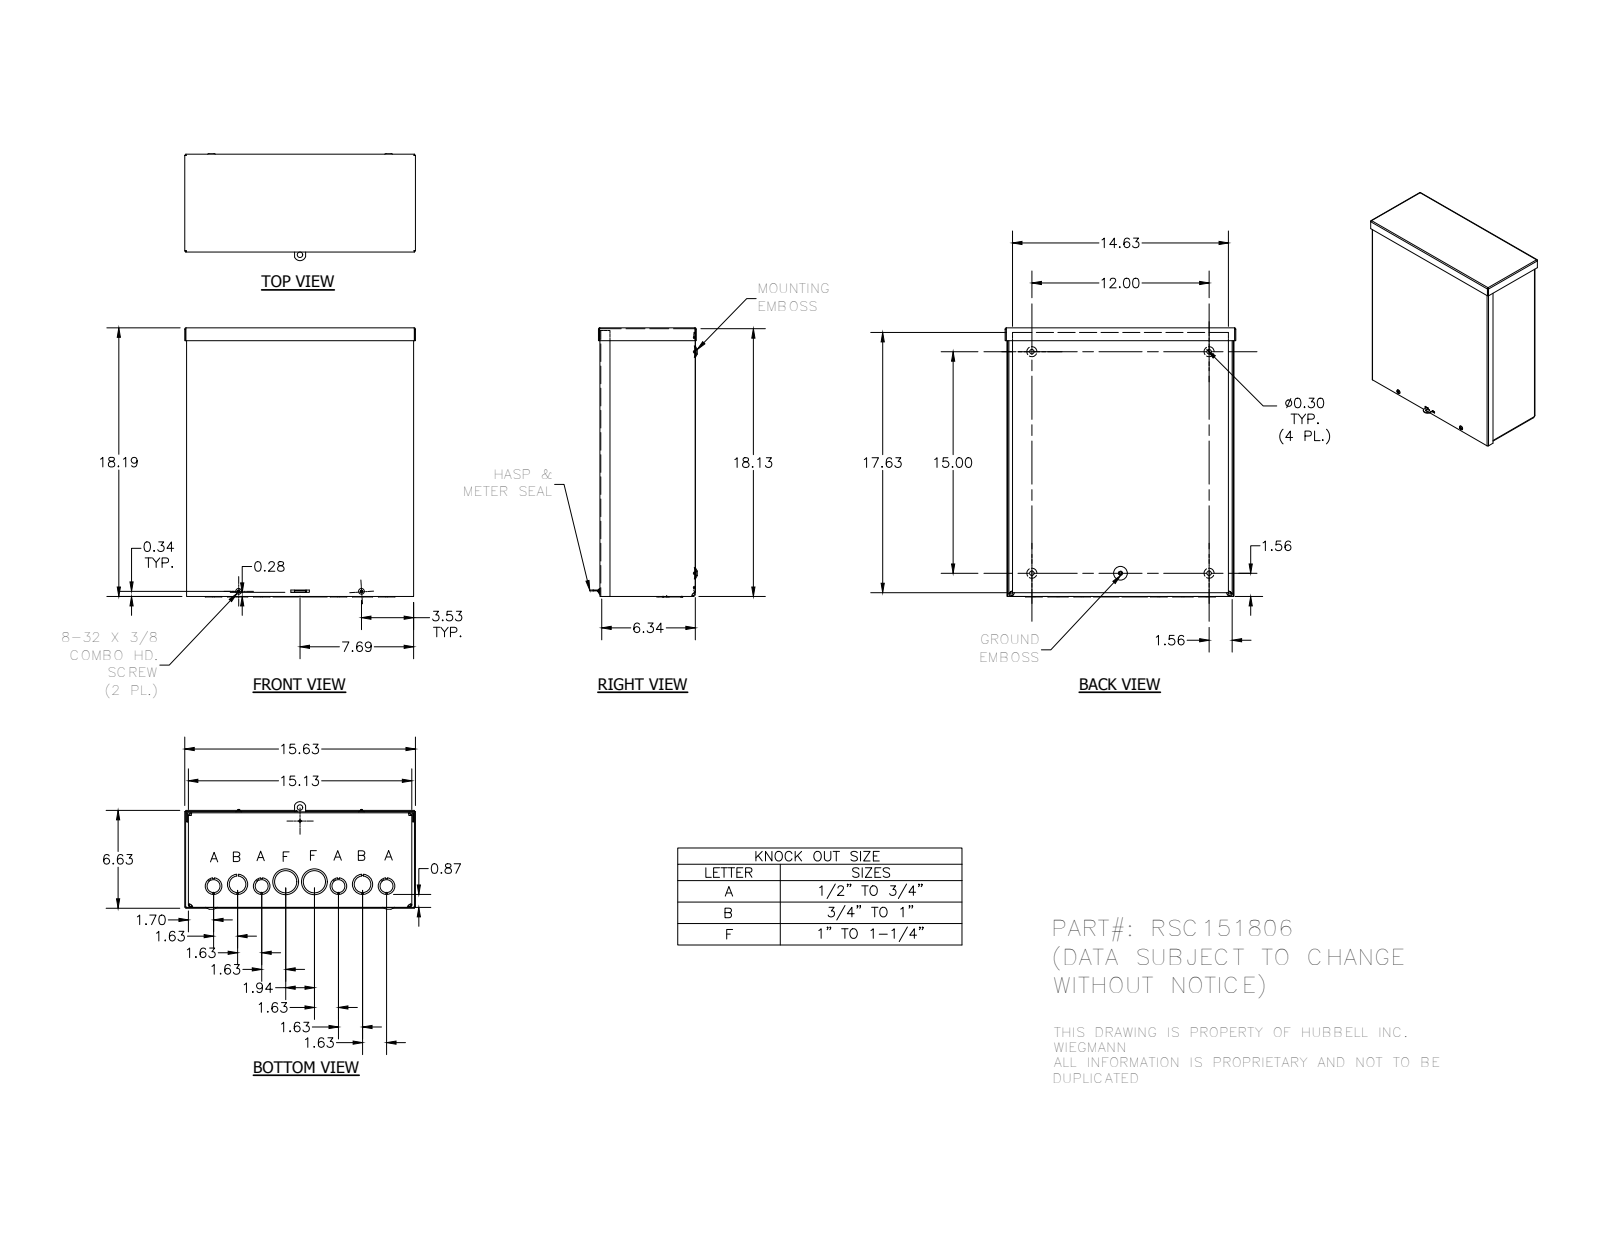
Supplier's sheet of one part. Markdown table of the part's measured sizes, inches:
| quantity | value |
| --- | --- |
| part name | RSC151806; RSC151806_WRAP; RSC1518_LID; RSC1506_CAP (+4 more) |
| STEP written by | Autodesk Inventor 2012 (AUTOMOTIVE_DESIGN) |
| units | inches |
| bodies | 7 solids, 619 faces (304 planar, 171 cylindrical, 144 other) |
| overall size | 18.281 × 15.625 × 7.125 |
| volume | 74.5 in³ |
| surface area | 2 426 in² |
| round holes (diameter × count) | 1.125 × 6, 0.3 × 4, 0.313 × 4, 0.875 × 4, 0.125 × 2, 0.148 × 2, 1.375 × 2, 1.5 × 2, 1.75 × 2, 0.156 × 1, 0.165 × 1, 0.375 × 1 |
| round bosses / shafts (diameter × count) | 0.384 × 2, 0.164 × 2, 0.229 × 1 |
| partial cylindrical surfaces (radius × count) | 0.01 × 15, 0.031 × 8, 0.093 × 8, 0.125 × 8, 0.187 × 8, 0.031 × 5, 0.021 × 4, 0.055 × 4 |
| main face-to-face distances | 0.062, 6.249, 6.187, 0.063, 0.062, 6.312, 6.25, 15.126, 18.126, 0.124 |
| hole center spacings | 1.635, 8.46, 1.656, 3.26, 3.264, 3.582, 4.898, 4.968 |
